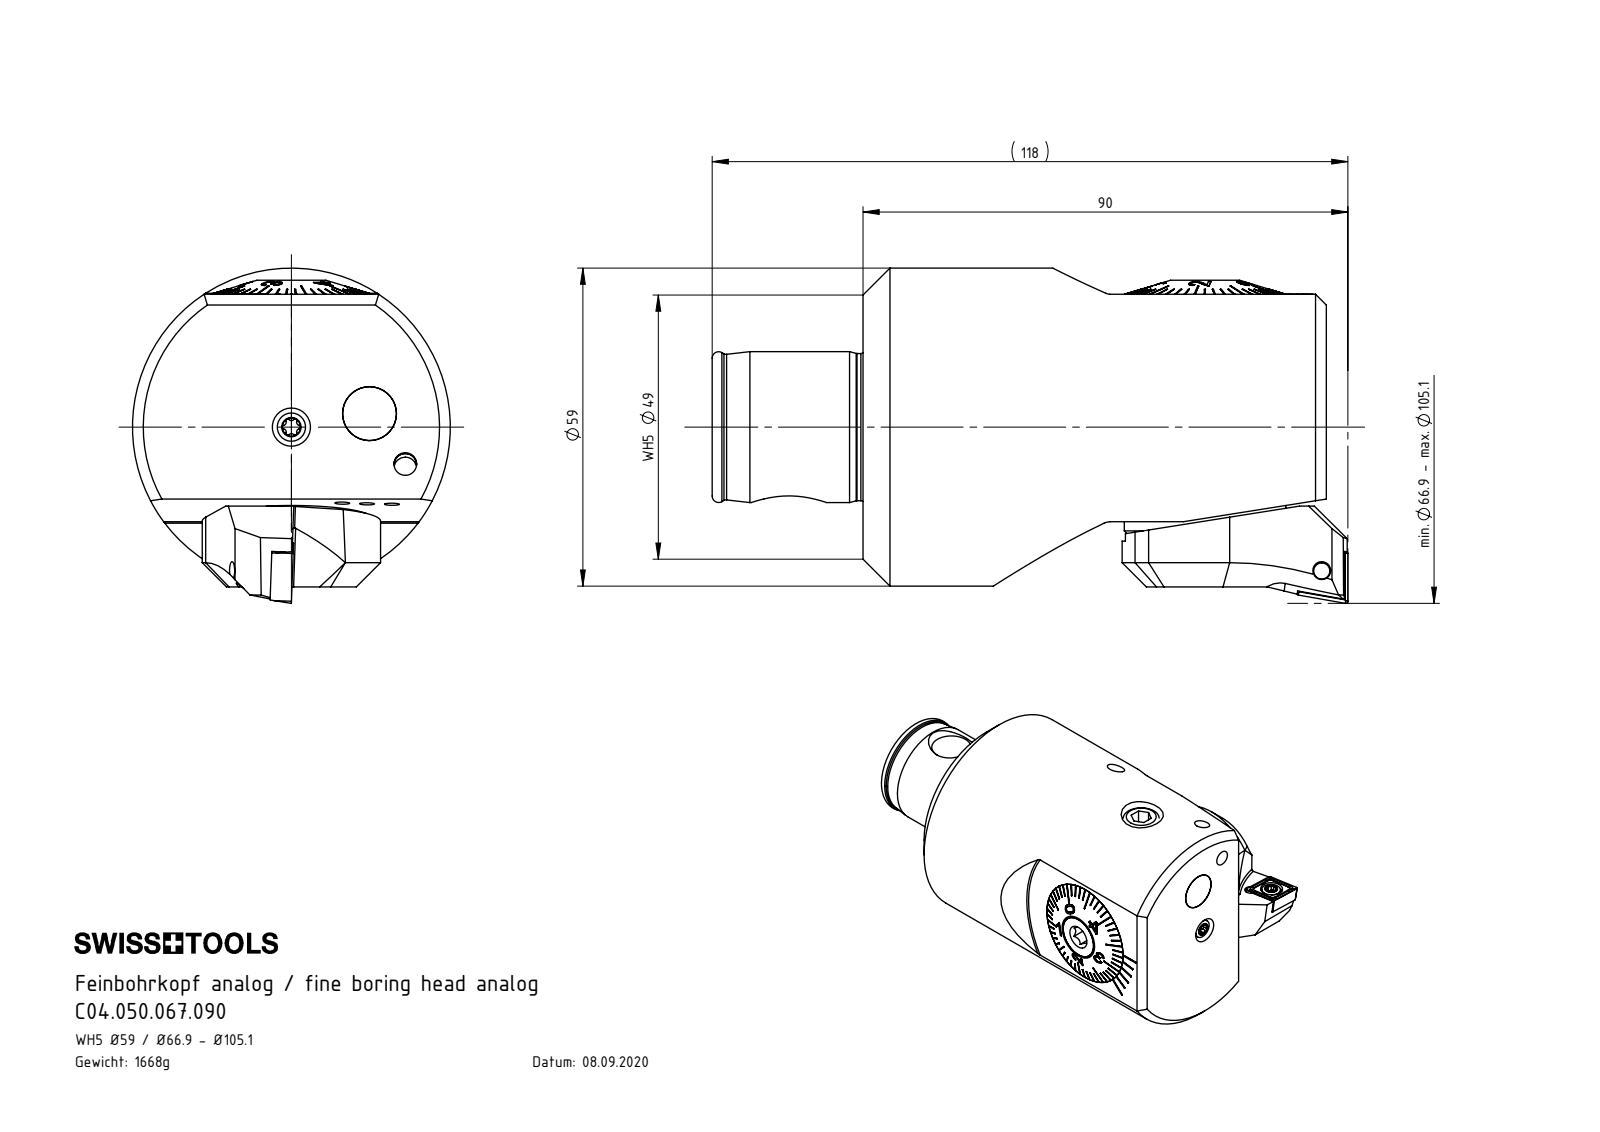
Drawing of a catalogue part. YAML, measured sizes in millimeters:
part_name: "A55-BG2.012.006_B; Klebstoff D10; WH5-F55.AA3.090_A; A55-BG2.011.016_D (+8 more)"
step_written_by: "SolidWorks 2017 (CONFIG_CONTROL_DESIGN)"
units: millimeters
bodies: {solids: 13, faces: 707, planar: 298, cylindrical: 133, other: 276}
overall_size: [114, 59.15, 59]
volume: 214843
surface_area: 45789
round_holes:
  - {diameter: 2.5, count: 3}
  - {diameter: 4.2, count: 3}
  - {diameter: 8.5, count: 3}
  - {diameter: 3.3, count: 2}
  - {diameter: 5, count: 1}
  - {diameter: 8, count: 1}
  - {diameter: 10, count: 1}
  - {diameter: 11.4, count: 1}
  - {diameter: 12, count: 1}
  - {diameter: 12.4, count: 1}
  - {diameter: 13, count: 1}
  - {diameter: 14, count: 1}
round_bosses_or_shafts:
  - {diameter: 10, count: 2}
  - {diameter: 59, count: 1}
  - {diameter: 30, count: 1}
  - {diameter: 29.98, count: 1}
  - {diameter: 29.9, count: 1}
  - {diameter: 28, count: 1}
  - {diameter: 27.3, count: 1}
  - {diameter: 25, count: 1}
partial_cylinders:
  - {radius: 0.34, count: 6}
  - {radius: 0.59, count: 6}
  - {radius: 2.5, count: 6}
  - {radius: 2, count: 4}
  - {radius: 3.2, count: 3}
  - {radius: 0.5, count: 2}
  - {radius: 1, count: 1}
  - {radius: 3.5, count: 1}
face_to_face_distances: [86, 35.7, 6.5, 42.2, 2.8, 38.5, 41, 2.5, 5.3, 1.2]
hole_center_spacings: [14.71, 17.33]
